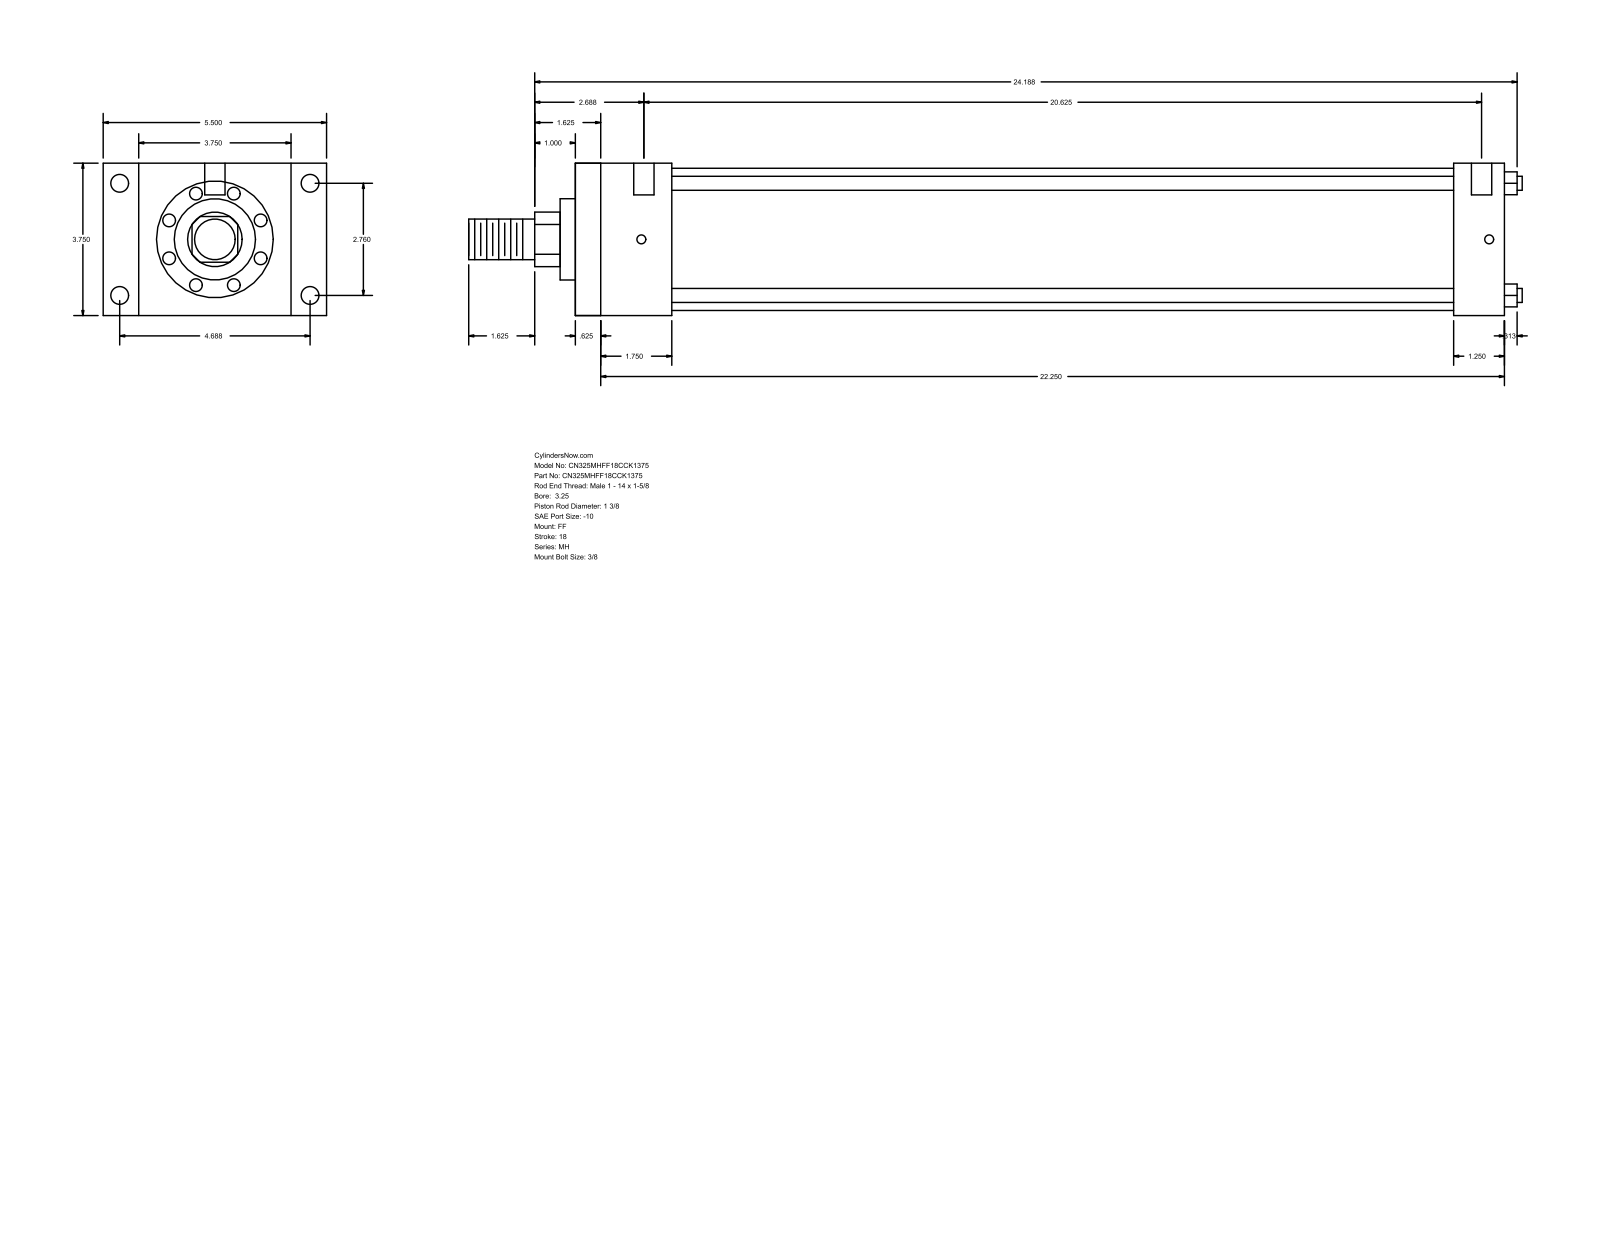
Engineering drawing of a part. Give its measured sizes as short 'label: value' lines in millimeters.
name: MH_FF__0325_1.375
written by: GSSL Pune (CONFIG_CONTROL_DESIGN)
unit: mm
bodies: 0 solids, 92 faces (64 planar, 28 cylindrical, 0 other)
size: 658.81 × 139.7 × 95.25
holes: 4× ⌀5.56, 4× ⌀11.13, 2× ⌀12.7
bosses: 4× ⌀8.76, 1× ⌀88.9, 1× ⌀50.8, 1× ⌀34.92, 1× ⌀25.4
rounds: 1× R17.06
face distances: 95.24, 581.02, 15.87, 565.15, 22.23, 117.47, 549.27, 533.4, 31.75, 60.32
hole spacings: 70.1, 119.06, 138.16, 530.23, 1.59, 4.76, 523.88, 525.47
